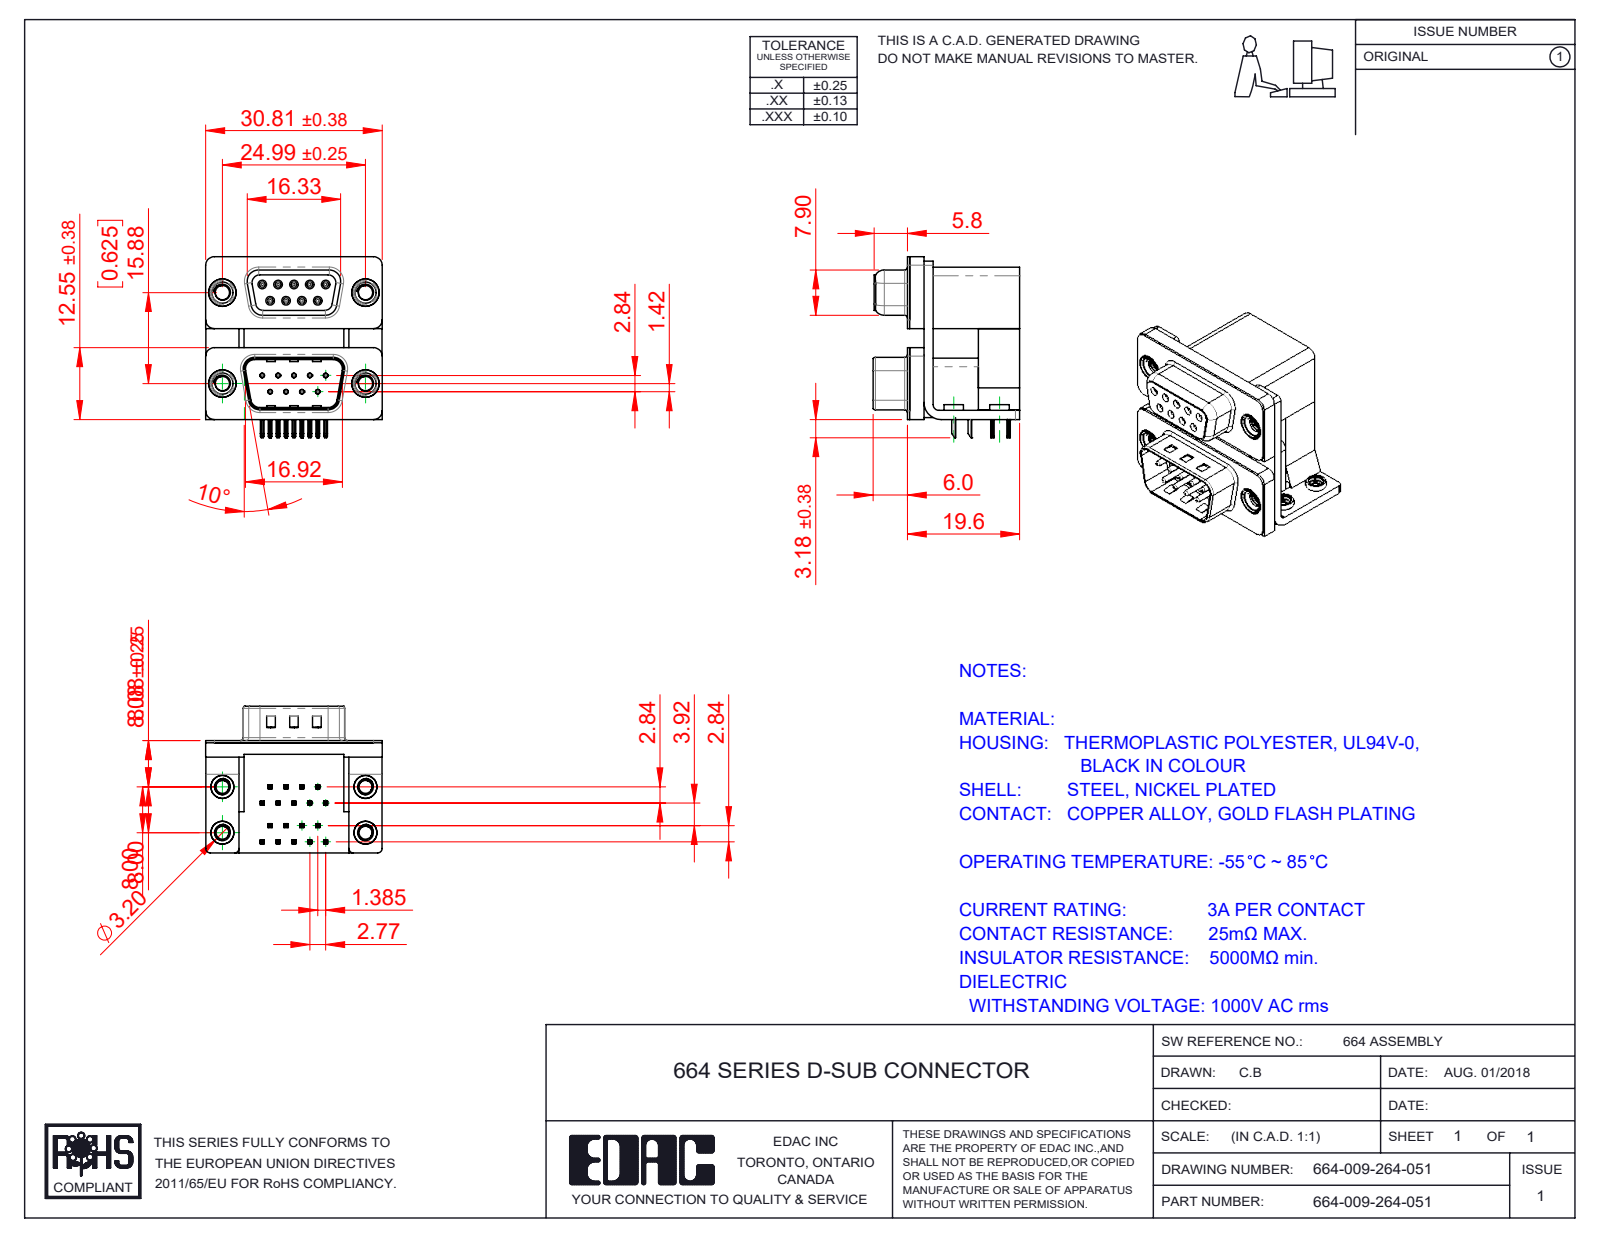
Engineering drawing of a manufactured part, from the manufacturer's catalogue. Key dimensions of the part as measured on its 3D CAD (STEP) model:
Part name (STEP PRODUCT): 664 Housing Upper_09 Contacts L; 664 Housing Lower_09 Contacts; 664 Mounting Bracket_ThruL; 664 Contact Top Lower (+8 more)
STEP written by: SolidWorks 2020 (CONFIG_CONTROL_DESIGN)
Units: millimetres
Bodies: 33 solids, 2673 faces (1275 planar, 779 cylindrical, 619 other)
Overall size (bounding box): 31.61 × 30.81 × 25.6
Volume: 10 345 mm³ · Surface area: 12 389 mm²
Round holes (diameter × count): ⌀0.8 ×18, ⌀0.35 ×9, ⌀0.9 ×9, ⌀2.26 ×4, ⌀2.5 ×4, ⌀2.75 ×4, ⌀3.2 ×4, ⌀3.5 ×4, ⌀4 ×4, ⌀4.8 ×4, ⌀5 ×4
Round bosses / shafts (diameter × count): ⌀1.2 ×9, ⌀0.75 ×9, ⌀4.9 ×4, ⌀4.75 ×4, ⌀4 ×4, ⌀3.9 ×4, ⌀3.4 ×4
Partial cylindrical surfaces — rounded edges, fillets, slot ends (radius × count): R0.1 ×72, R0.15 ×36, R0.25 ×36, R0.12 ×18, R0.35 ×18, R1.5 ×13, R0.5 ×12, R1.35 ×10
Main face-to-face distances: 0.4, 2.5, 16.7, 19.2, 19.6, 2.9, 7.2, 9.5, 12, 12.4
Hole centre spacings: 3.16, 2.77, 16.12, 15.88, 5.54, 16.82, 13.11, 18.77
